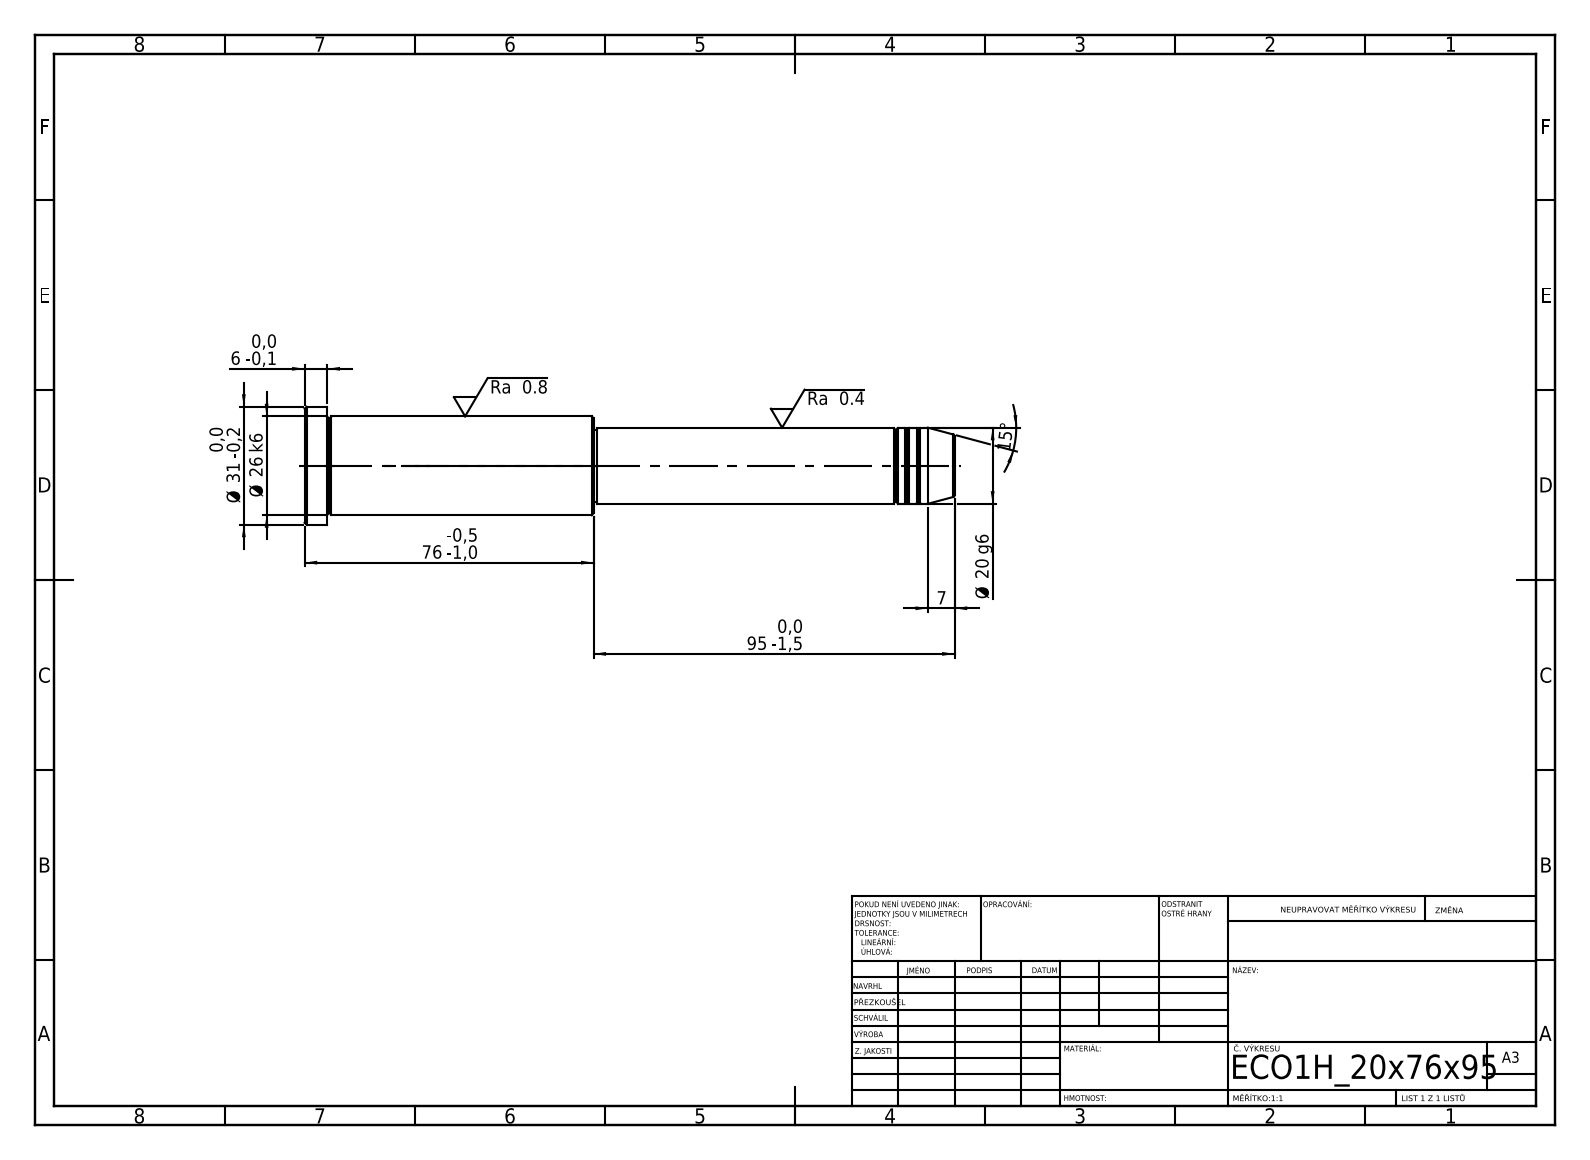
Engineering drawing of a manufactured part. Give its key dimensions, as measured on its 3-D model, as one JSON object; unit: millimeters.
{"step_written_by": "SolidWorks 2019 (CONFIG_CONTROL_DESIGN)", "units": "millimeters", "bodies": {"solids": 1, "faces": 43, "planar": 5, "cylindrical": 14, "other": 24}, "overall_size": [171, 31, 31], "volume_mm3": 70994, "surface_area_mm2": 13787, "round_bosses_or_shafts": [[31, 1], [26, 1], [20, 1], [19, 1]], "face_to_face_distances": [6, 70, 76, 95, 165, 171, 94, 1, 71, 77]}
